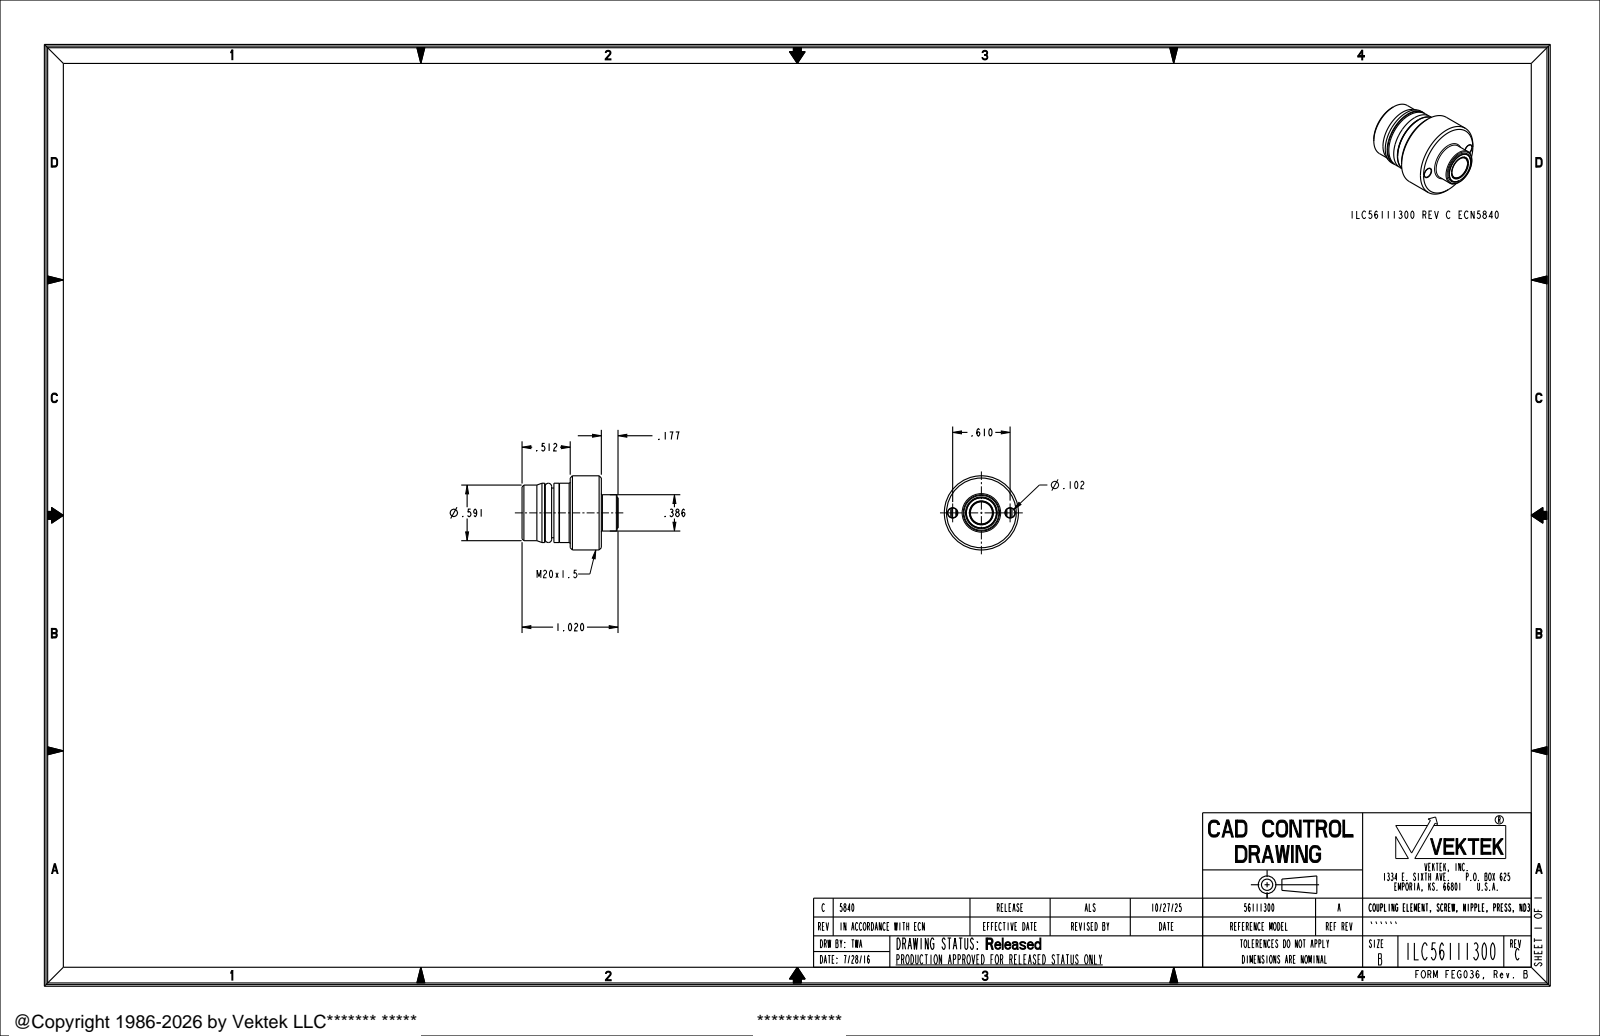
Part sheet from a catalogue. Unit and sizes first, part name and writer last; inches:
Units: inches
Overall size (bounding box): 1.02 × 0.787 × 0.787
Round holes (diameter × count): ⌀0.102 ×2, ⌀0.242 ×1, ⌀0.248 ×1, ⌀0.394 ×1, ⌀0.417 ×1
Round bosses / shafts (diameter × count): ⌀0.079 ×6, ⌀0.047 ×2, ⌀0.787 ×1, ⌀0.63 ×1, ⌀0.591 ×1, ⌀0.528 ×1, ⌀0.386 ×1
Partial cylindrical surfaces — rounded edges, fillets, slot ends (radius × count): R0.059 ×4, R0.182 ×1
Main face-to-face distances: 0.843, 0.512, 0.331, 0.177, 0.776, 0.217, 0.294, 0.625, 0.394, 0.176
Hole centre spacings: 0.305, 0.61
Volume: 0.007 in³ · Surface area: 5.152 in²
Bodies: 1 solid, 101 faces (13 planar, 52 cylindrical, 36 other)
Part name (STEP PRODUCT): ILC56111300
STEP written by: PRO/ENGINEER BY PARAMETRIC TECHNOLOGY CORPORATION, 2013320 (AUTOMOTIVE_DESIGN)
